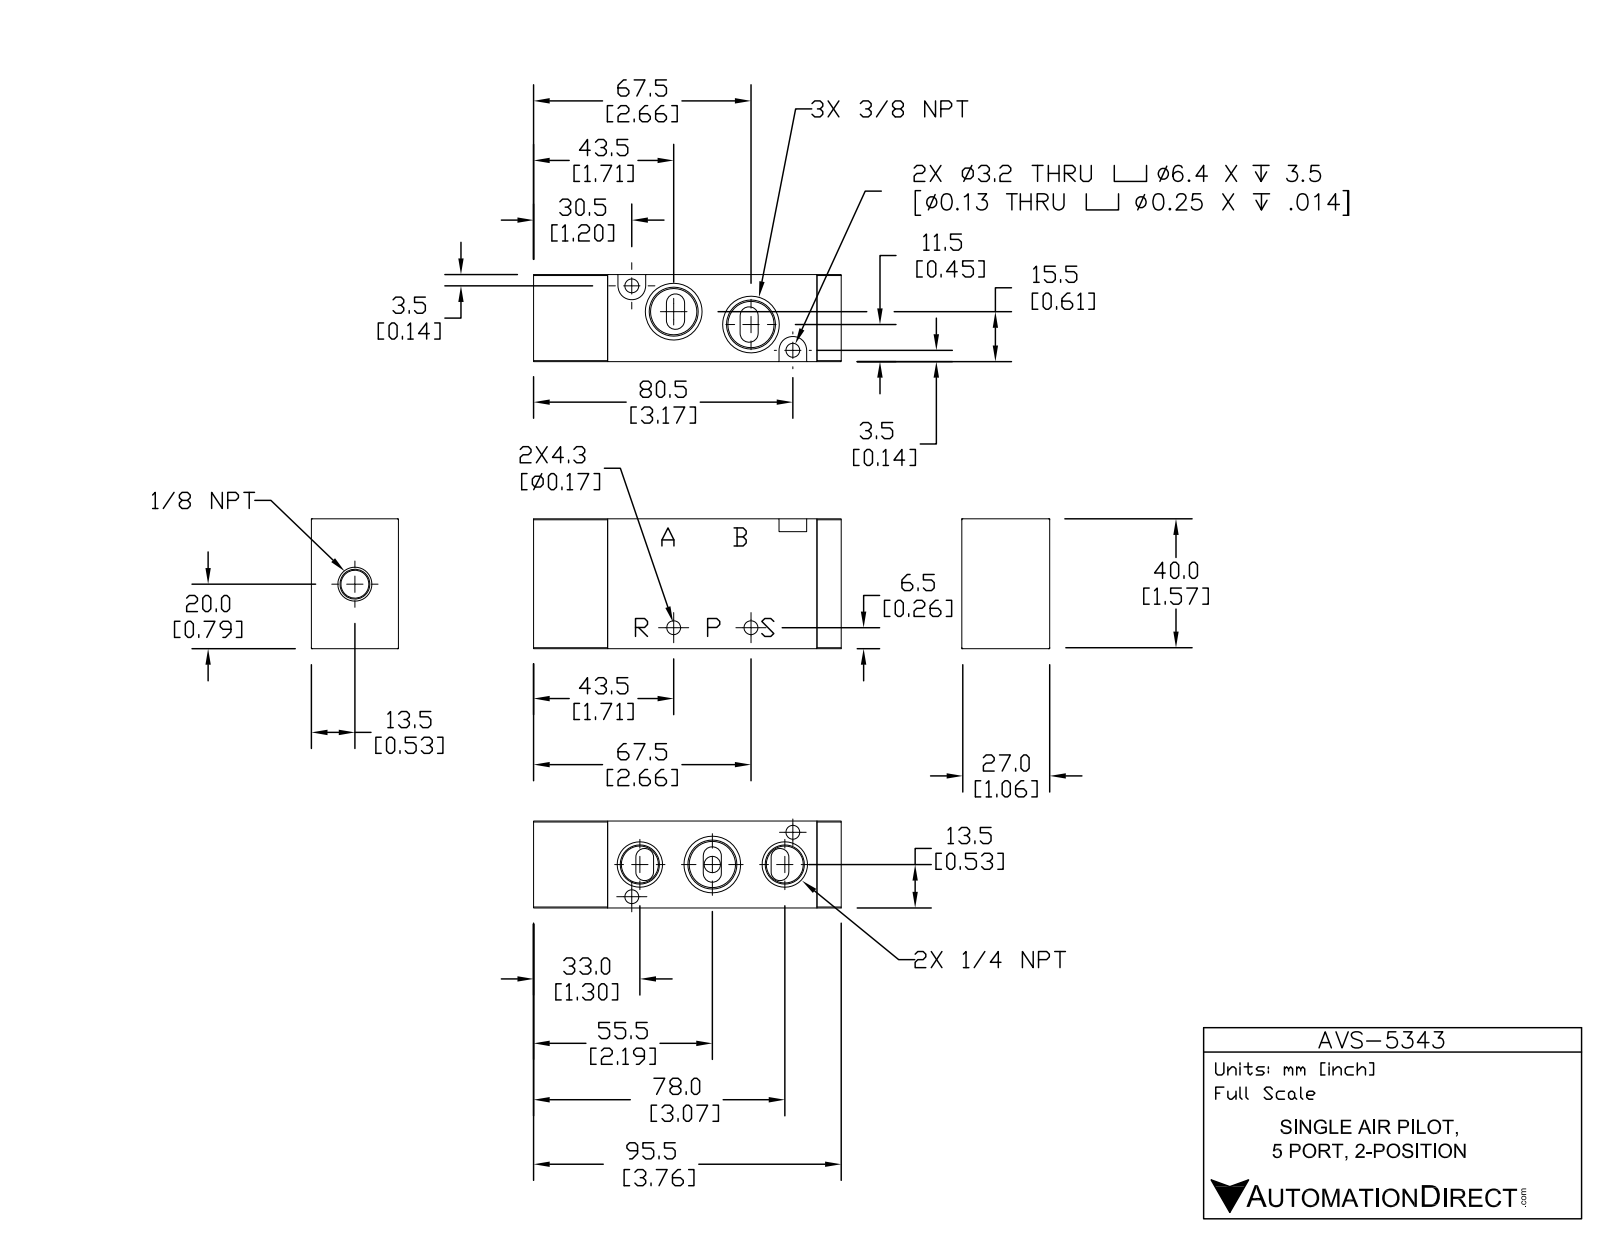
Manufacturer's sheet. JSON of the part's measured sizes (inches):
{"part_name": "AVS-5343", "step_written_by": "SolidWorks 2021 (CONFIG_CONTROL_DESIGN)", "units": "inches", "bodies": {"solids": 3, "faces": 106, "planar": 46, "cylindrical": 36, "other": 24}, "overall_size": [3.76, 1.575, 1.063], "volume_in3": 5.505, "surface_area_in2": 37.57, "round_holes": [[0.169, 4], [0.199, 1]], "partial_cylinders_radius": [[0.111, 6], [0.012, 4], [0.108, 4], [0.169, 2]], "face_to_face_distances": [1.063, 2.559, 1.575, 0.295, 2.854, 3.76, 3.465, 0.906, 0.461, 1.114], "hole_center_spacings": [1.06, 0.945, 2.12]}
